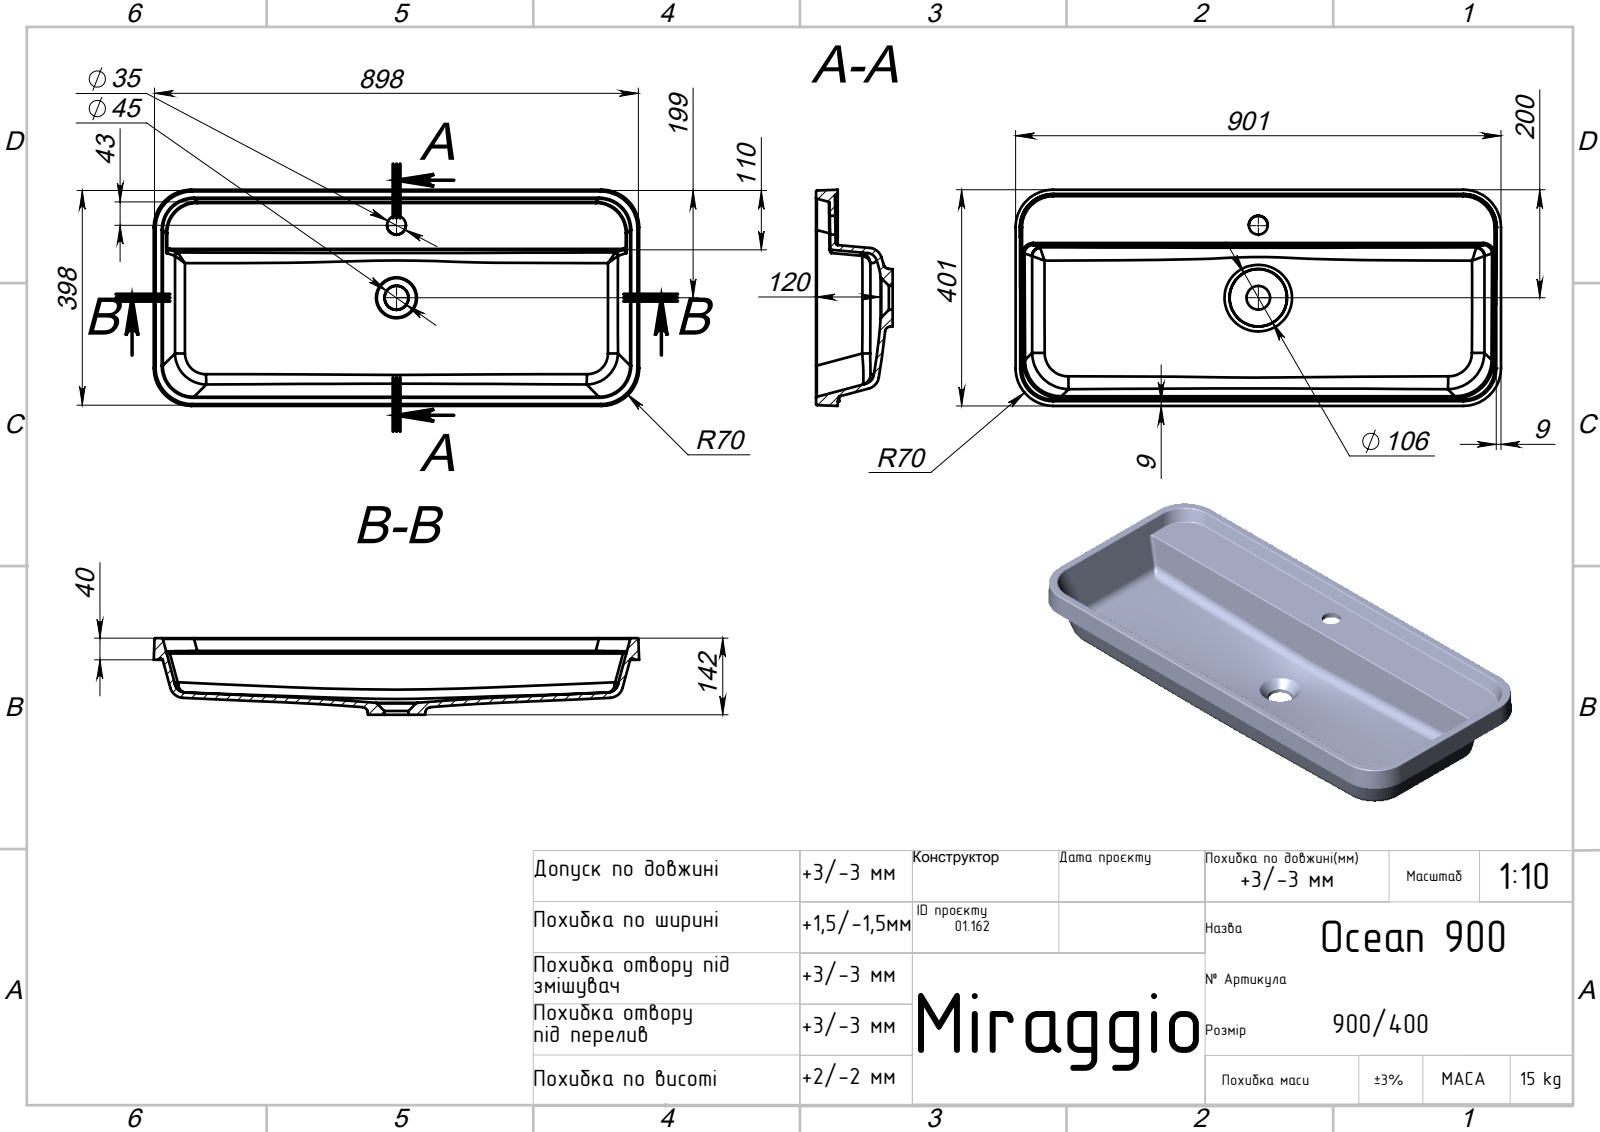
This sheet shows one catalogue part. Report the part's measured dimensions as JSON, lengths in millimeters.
{"part_name": "Ocean 900", "step_written_by": "SolidWorks 2020 (AUTOMOTIVE_DESIGN)", "units": "millimeters", "bodies": {"solids": 1, "faces": 121, "planar": 22, "cylindrical": 42, "other": 57}, "overall_size": [900, 400, 142], "volume_mm3": 6001000, "surface_area_mm2": 1106000, "round_holes": [[35, 1]], "partial_cylinders_radius": [[5, 16], [70, 6], [2, 4], [60, 4], [62, 4], [1, 3], [6, 2], [16, 2]], "face_to_face_distances": [10, 9.99, 5, 15, 40, 35, 25, 102, 107, 117]}
